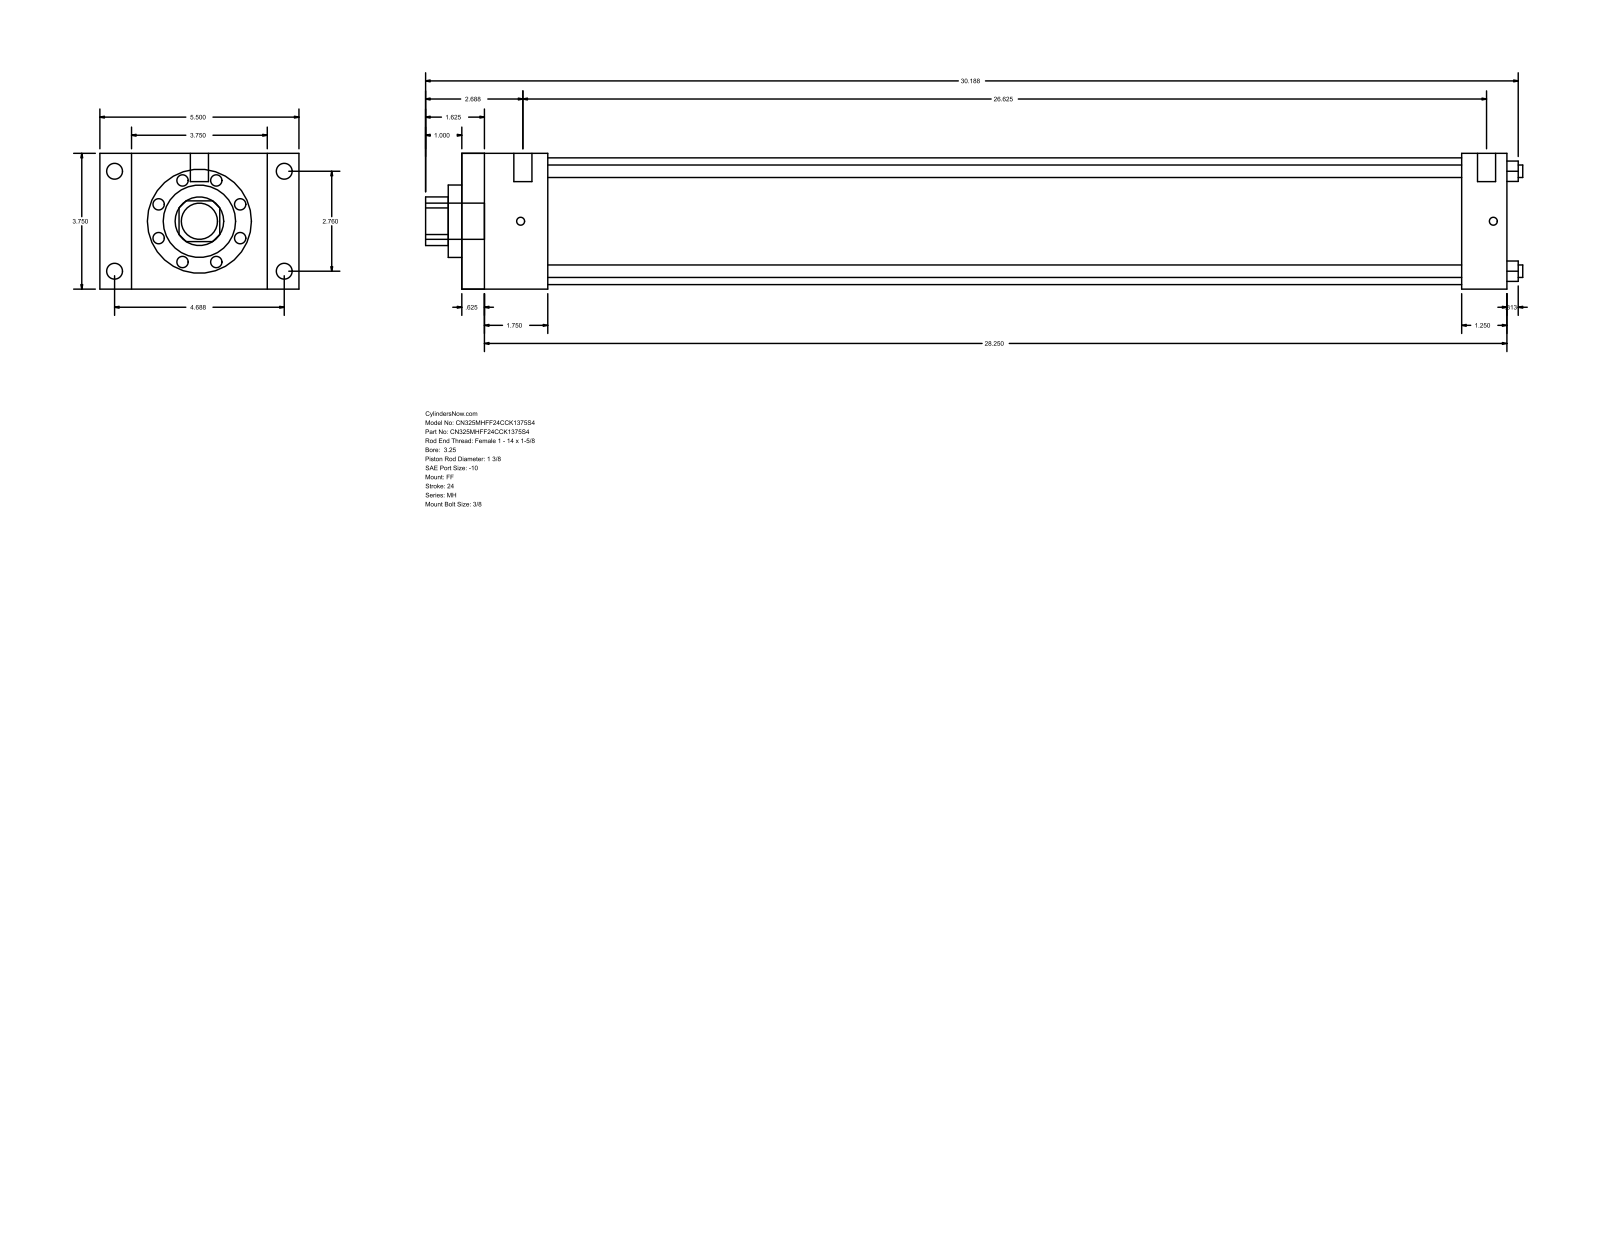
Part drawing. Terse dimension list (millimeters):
name: MH_FF__0325_1.375
written by: GSSL Pune (CONFIG_CONTROL_DESIGN)
unit: mm
bodies: 0 solids, 92 faces (64 planar, 28 cylindrical, 0 other)
size: 769.94 × 139.7 × 95.25
holes: 4× ⌀8.76, 1× ⌀34.92, 1× ⌀50.8, 1× ⌀88.9
bosses: 4× ⌀11.13, 4× ⌀5.56, 2× ⌀12.7, 1× ⌀25.4
rounds: 1× R17.06
face distances: 95.24, 733.43, 15.87, 717.56, 22.23, 117.47, 701.68, 685.81, 31.75, 60.32
hole spacings: 49.57, 70.1, 99.14
